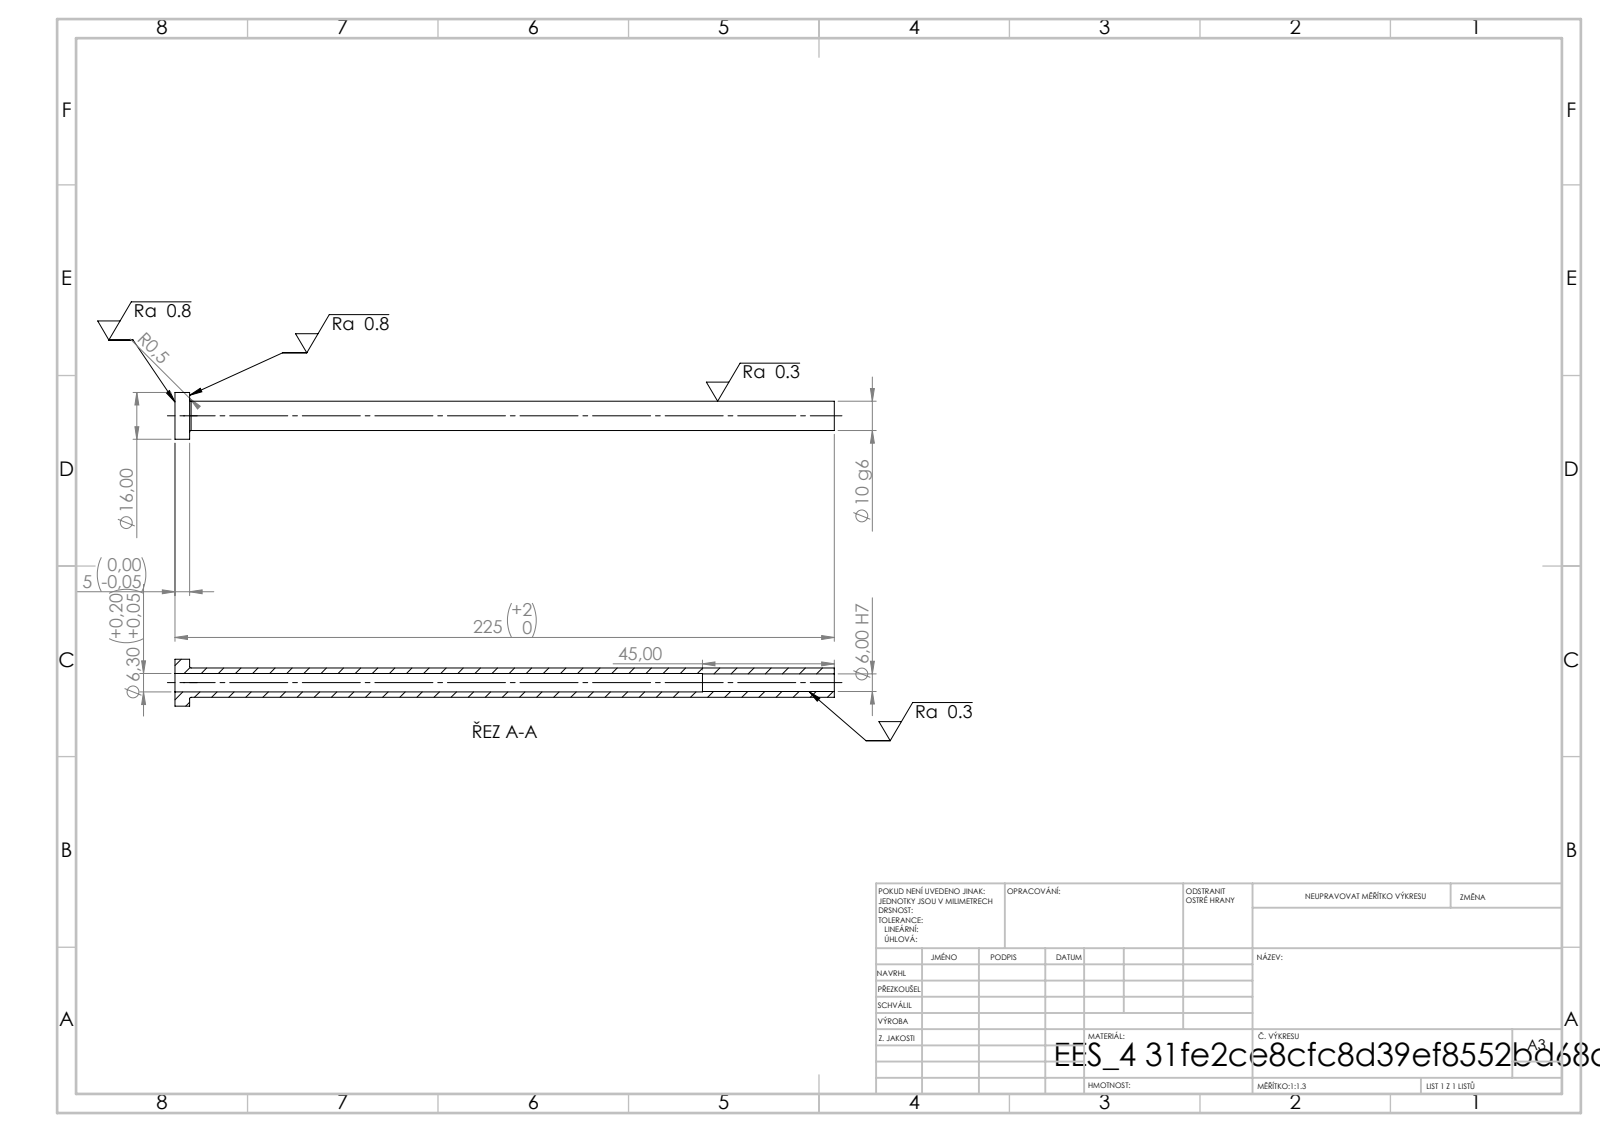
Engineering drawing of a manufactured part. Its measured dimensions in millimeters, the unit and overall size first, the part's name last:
Units: millimetres
Overall size (bounding box): 225 × 16 × 16
Round holes (diameter × count): ⌀6 ×1, ⌀6.3 ×1
Round bosses / shafts (diameter × count): ⌀16 ×1, ⌀10 ×1
Main face-to-face distances: 5, 225, 220, 180, 175, 45
Volume: 11 402 mm³ · Surface area: 11 913 mm²
Bodies: 1 solid, 14 faces (4 planar, 8 cylindrical, 2 other)
STEP written by: SolidWorks 2019 (CONFIG_CONTROL_DESIGN)
